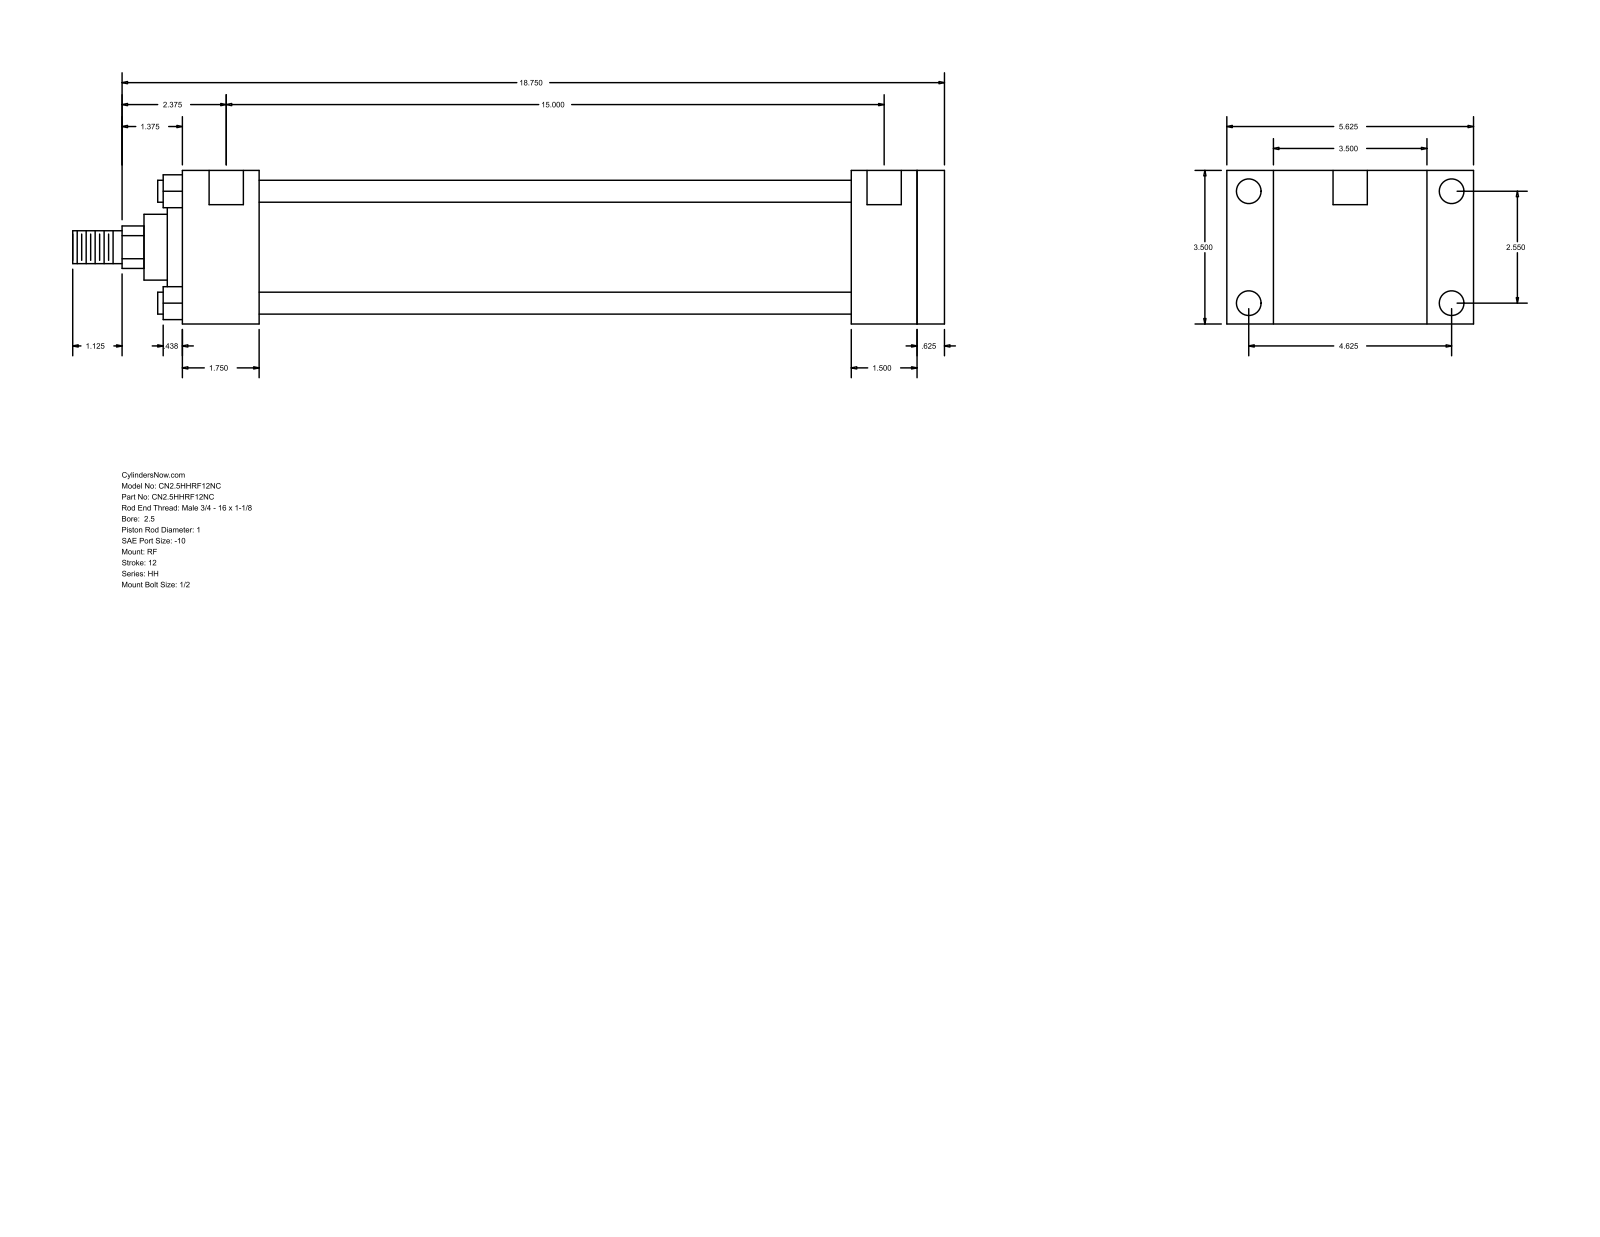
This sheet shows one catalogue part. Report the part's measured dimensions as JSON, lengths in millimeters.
{"part_name": "HH_RF__0250_1", "step_written_by": "GSSL Pune (CONFIG_CONTROL_DESIGN)", "units": "millimeters", "bodies": {"solids": 0, "faces": 94, "planar": 65, "cylindrical": 29, "other": 0}, "overall_size": [504.82, 142.88, 88.9], "round_holes": [[5.56, 4], [14.3, 4], [19.84, 2]], "round_bosses_or_shafts": [[12.7, 4], [73.03, 1], [60.33, 1], [38.1, 1], [25.4, 1], [19.05, 1]], "partial_cylinders_radius": [[12.29, 1]], "face_to_face_distances": [88.9, 15.87, 425.46, 441.33, 44.46, 381, 396.87, 387.35, 342.89, 38.11], "hole_center_spacings": [1.59, 64.76, 117.48, 134.15, 382.58, 384.17, 380.99]}
